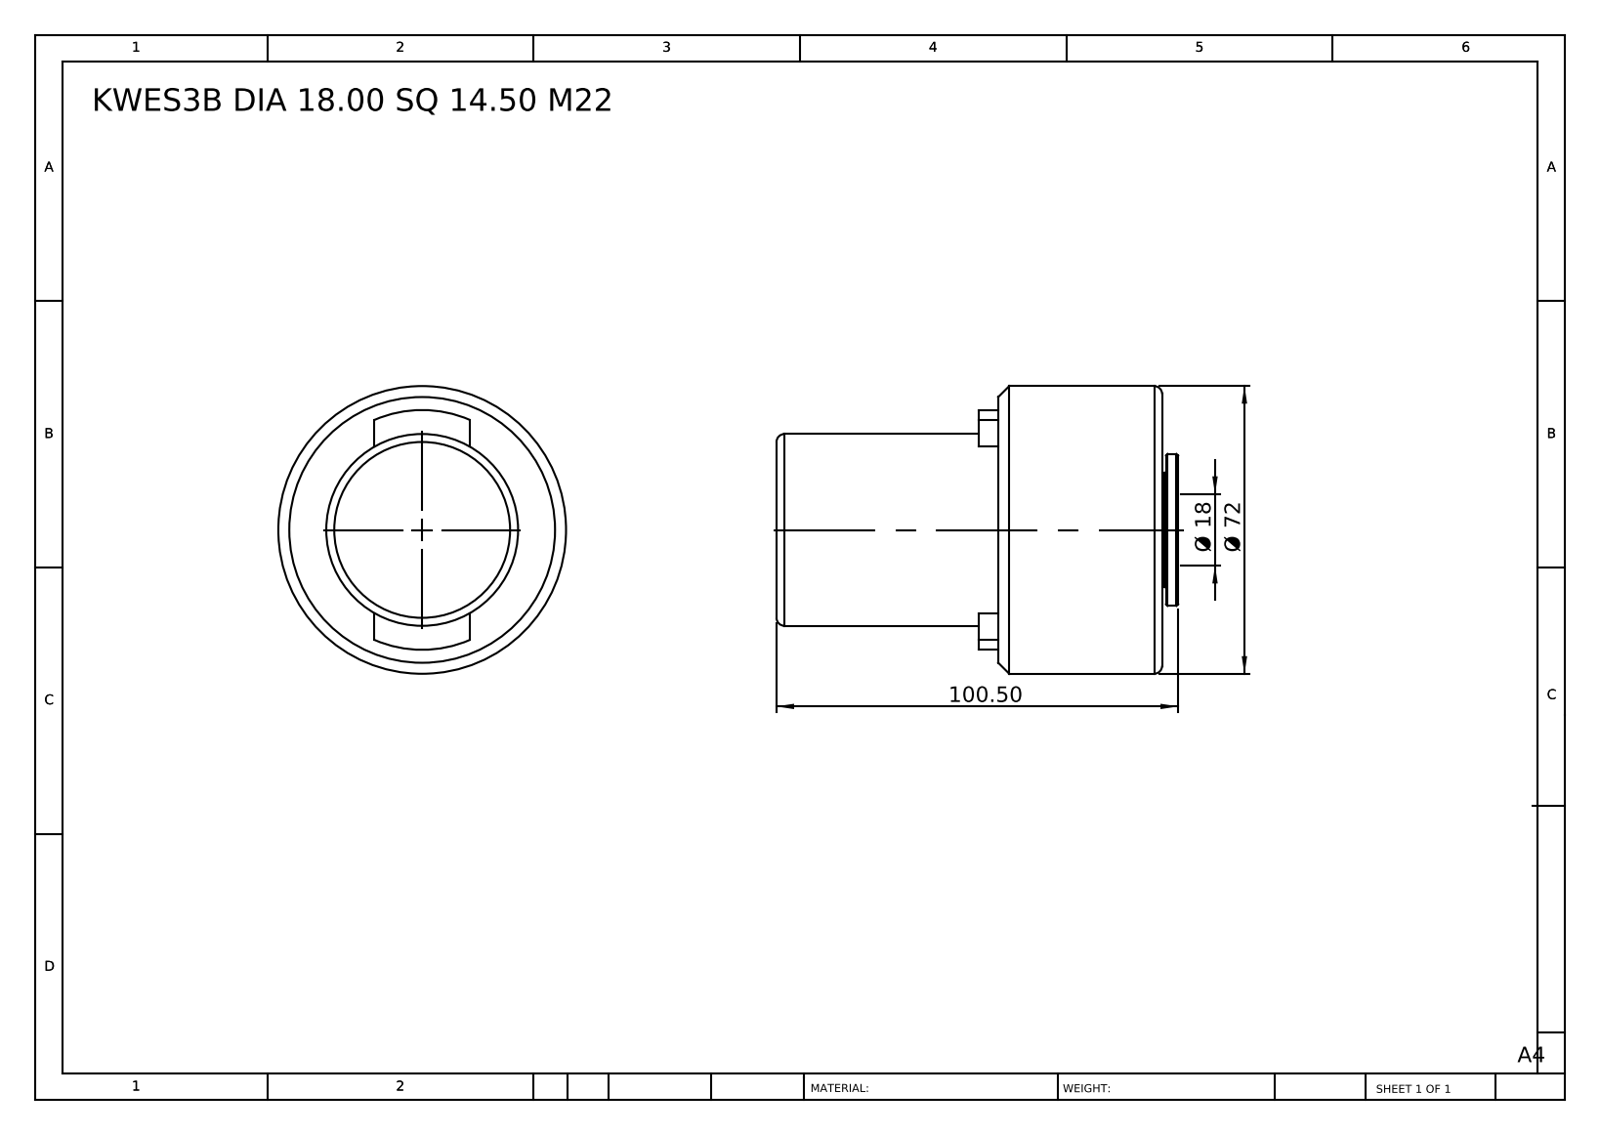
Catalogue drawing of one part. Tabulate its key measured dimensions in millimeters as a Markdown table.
| quantity | value |
| --- | --- |
| part name | KWES3B DIA 18.00 SQ 14.50 5-8'''''''' G(BSP) |
| STEP written by | SolidWorks 2014 (CONFIG_CONTROL_DESIGN) |
| units | millimeters |
| bodies | 1 solid, 39 faces (12 planar, 13 cylindrical, 14 other) |
| overall size | 100.5 × 72 × 72 |
| volume | 261 536 mm³ |
| surface area | 28 829 mm² |
| round holes (diameter × count) | 18 × 1 |
| round bosses / shafts (diameter × count) | 72 × 1, 48 × 1, 38 × 1, 28.5 × 1 |
| partial cylindrical surfaces (radius × count) | 30 × 1 |
| main face-to-face distances | 96.5, 55.5, 41, 100.5, 45, 4, 5, 97.5, 42, 1 |
